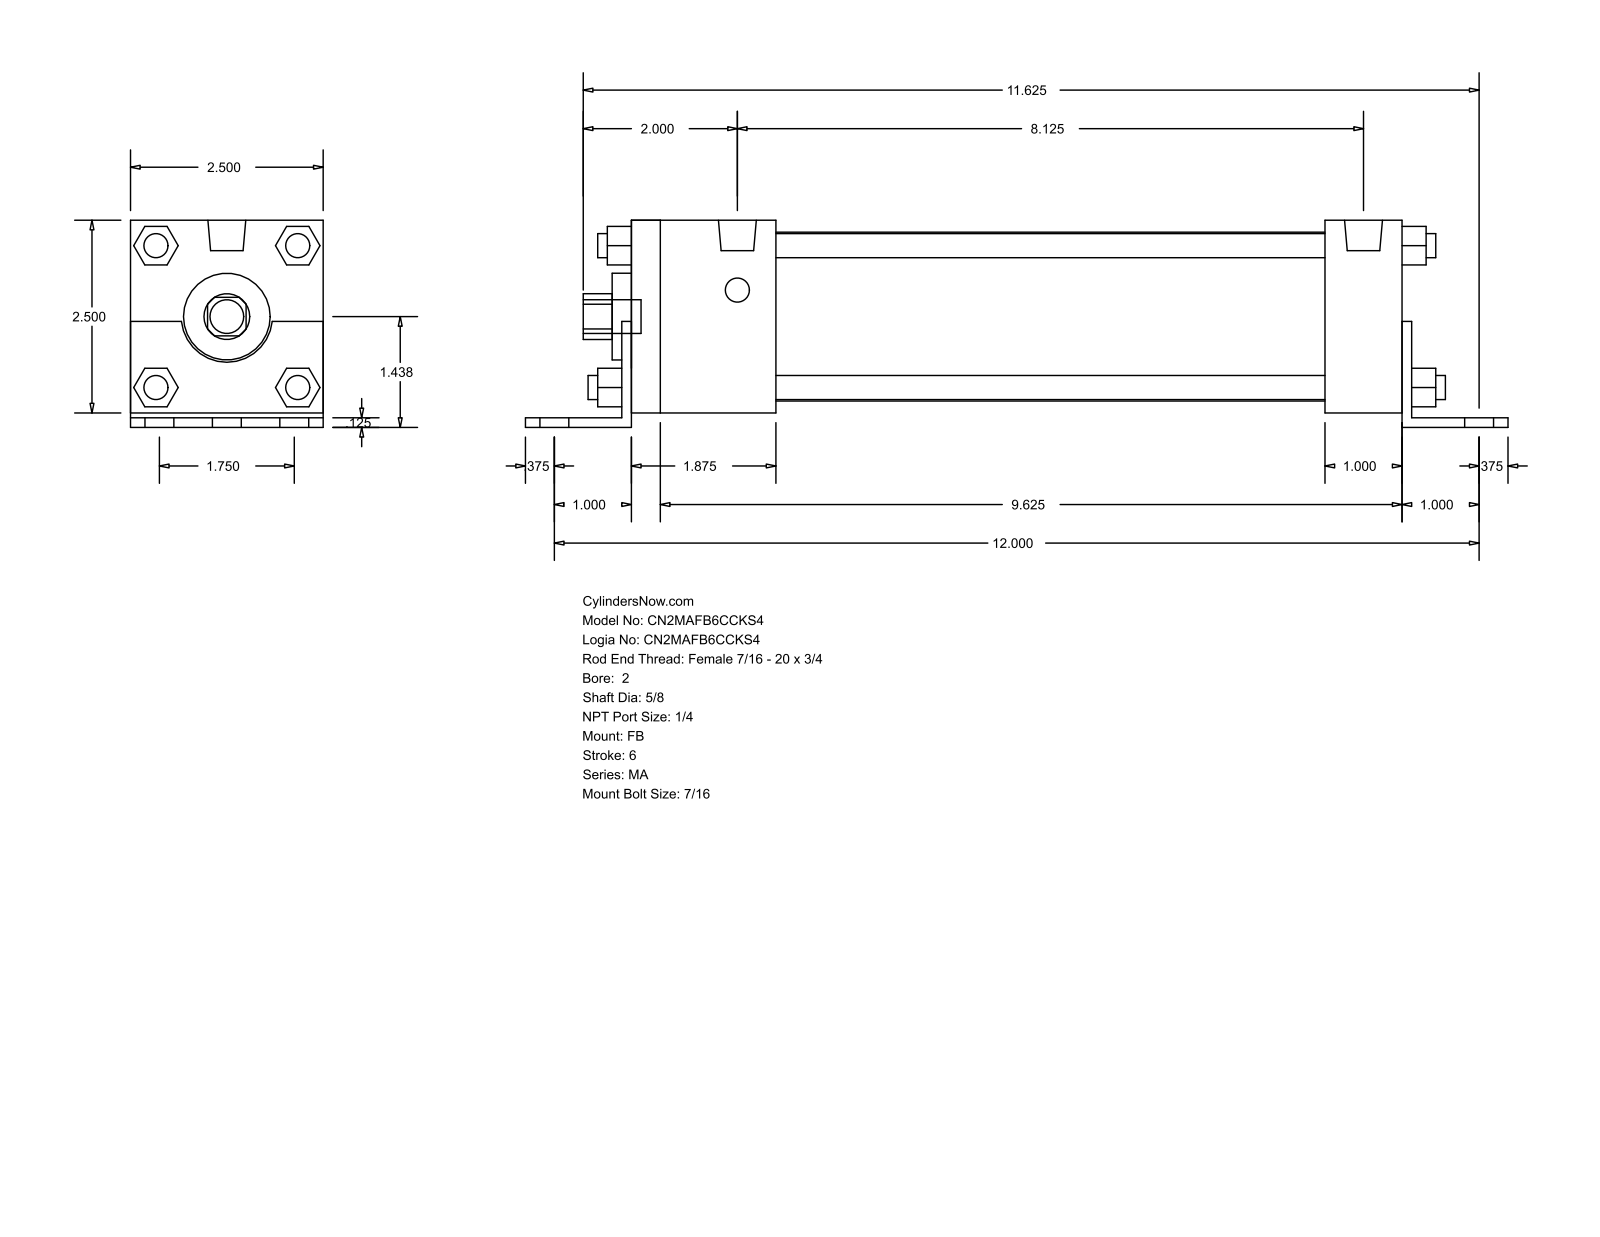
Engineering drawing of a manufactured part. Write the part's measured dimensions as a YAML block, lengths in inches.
part_name: "MA_FB__0200_0.625"
step_written_by: "GSSL Pune (CONFIG_CONTROL_DESIGN)"
units: inches
bodies: {solids: 0, faces: 140, planar: 105, cylindrical: 35, other: 0}
overall_size: [12.75, 2.687, 2.5]
round_holes:
  - {diameter: 0.625, count: 1}
  - {diameter: 1.125, count: 1}
  - {diameter: 2.19, count: 1}
round_bosses_or_shafts:
  - {diameter: 0.313, count: 8}
  - {diameter: 0.437, count: 7}
  - {diameter: 0.492, count: 2}
partial_cylinders:
  - {radius: 0.297, count: 1}
  - {radius: 0.593, count: 1}
face_to_face_distances: [2.5, 0.125, 0.187, 2.687, 0.063, 2.563, 10, 10.25, 0.125, 10.125]
